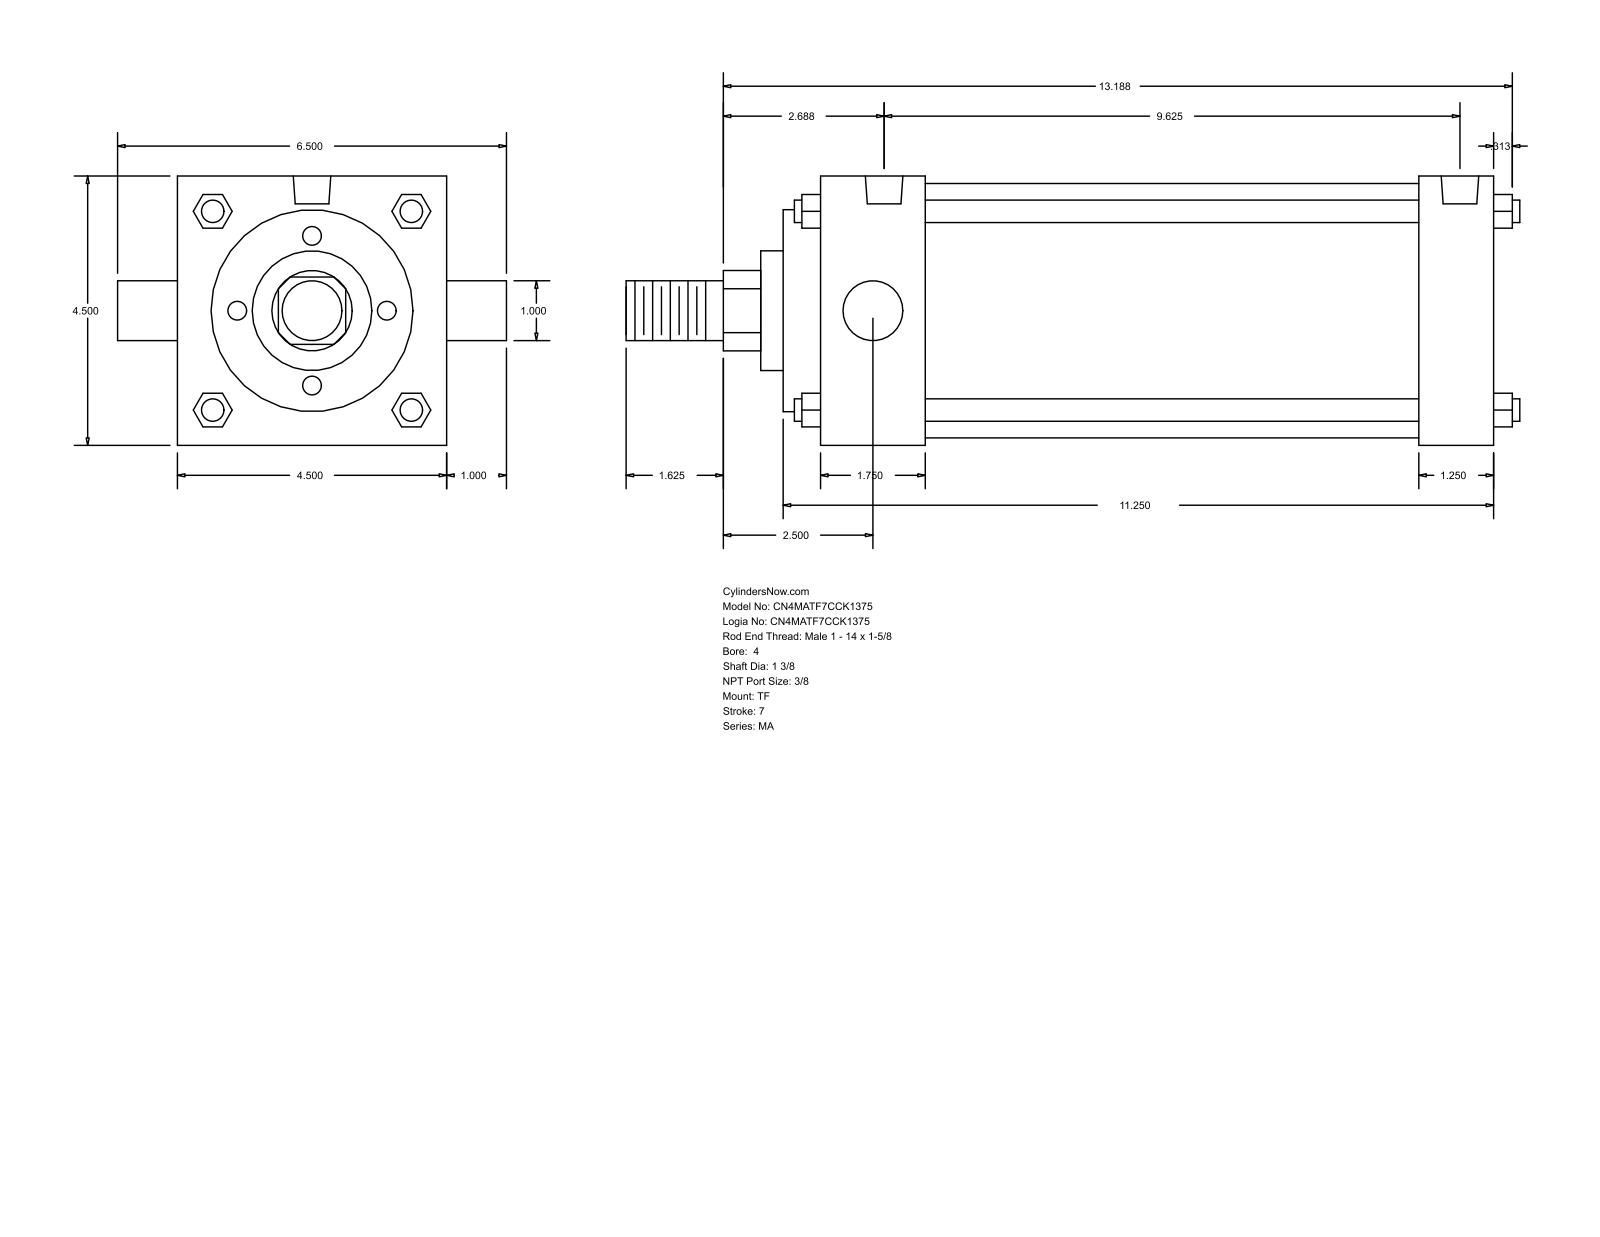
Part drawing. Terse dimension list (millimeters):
name: MA_TF__0400_1.375
written by: GSSL Pune (CONFIG_CONTROL_DESIGN)
unit: mm
bodies: 0 solids, 122 faces (93 planar, 29 cylindrical, 0 other)
size: 379.41 × 165.1 × 114.3
holes: 3× ⌀11.11, 2× ⌀15.93
bosses: 4× ⌀9.53, 2× ⌀25.4, 1× ⌀107.95, 1× ⌀85.72, 1× ⌀50.8, 1× ⌀34.92
rounds: 1× R17.06
face distances: 114.3, 285.75, 301.62, 15.87, 269.87, 254, 31.75, 60.32, 44.45, 209.55
hole spacings: 4.76, 4.77, 234.95, 239.71, 239.72, 244.48
